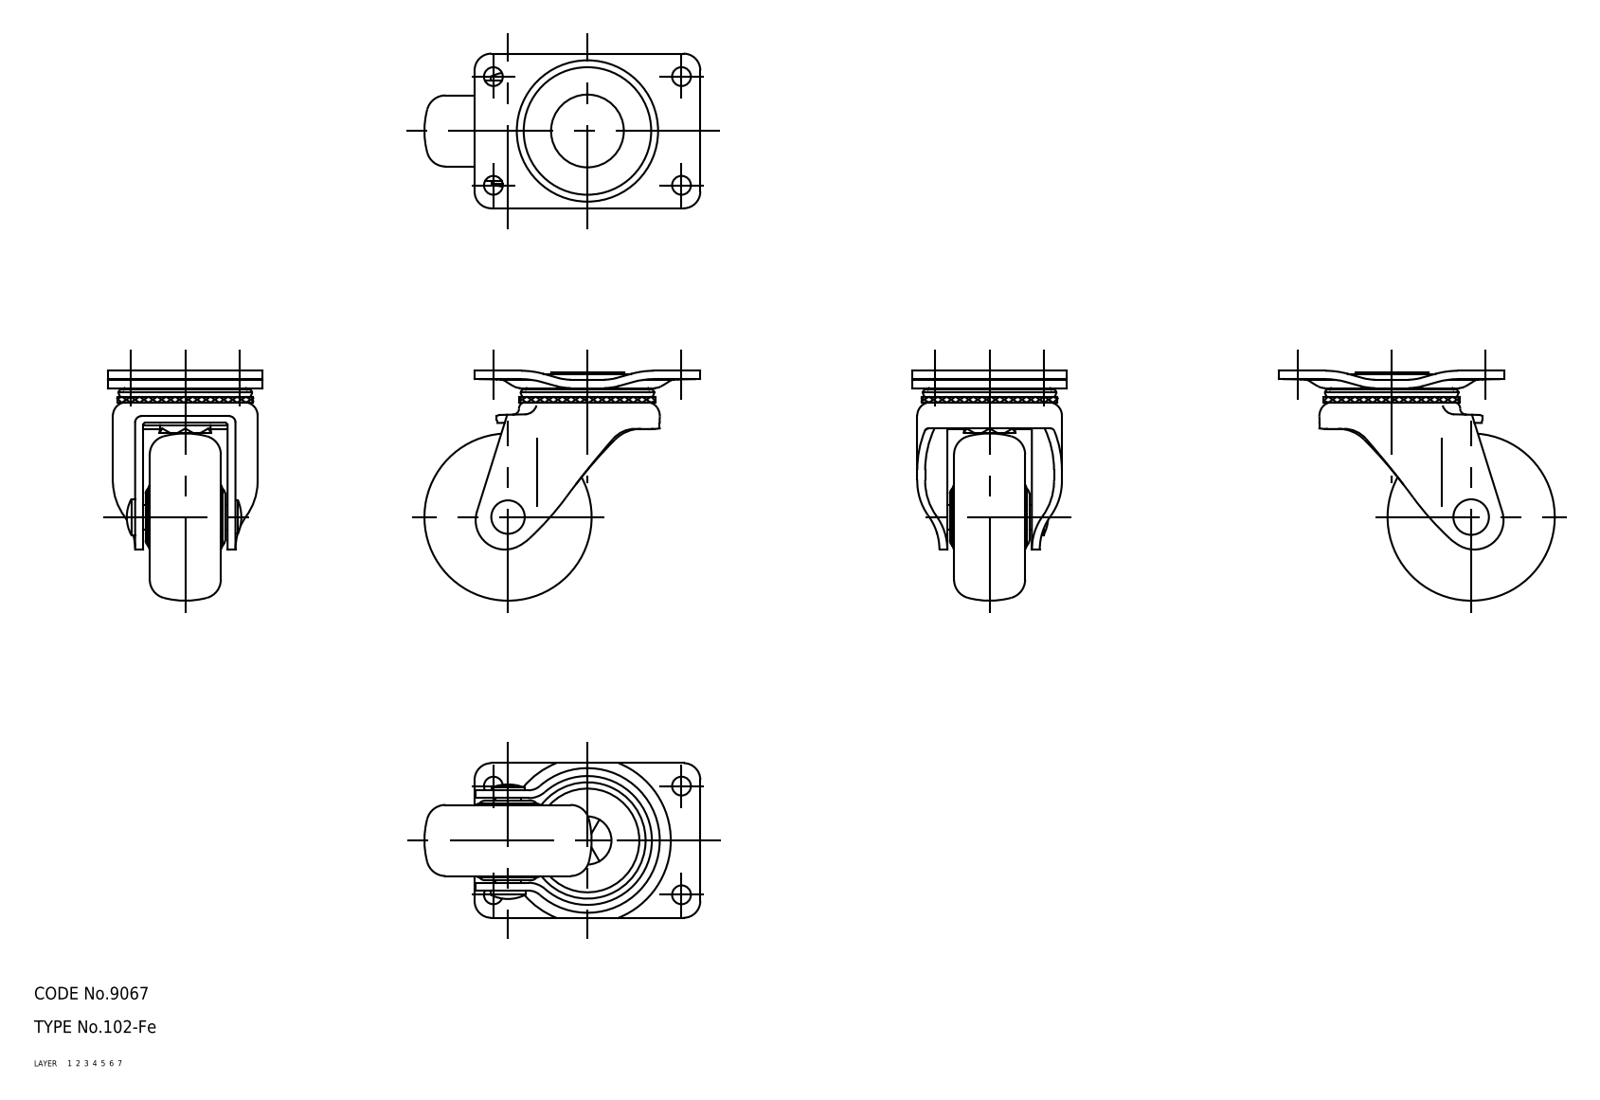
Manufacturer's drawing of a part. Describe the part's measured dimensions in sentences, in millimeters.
The part is named "wheel; mounting plate; main shaft; axle (+1 more)". Its 3-D file was written by "CADfix (AUTOMOTIVE_DESIGN)". It is 5 solids with 259 faces: 0 planar, 0 cylindrical and 259 other. Overall it measures 66 by 55 by 37 millimeters. Its volume is 34 064 cubic millimeters and its surface area 17 178 square millimeters.
